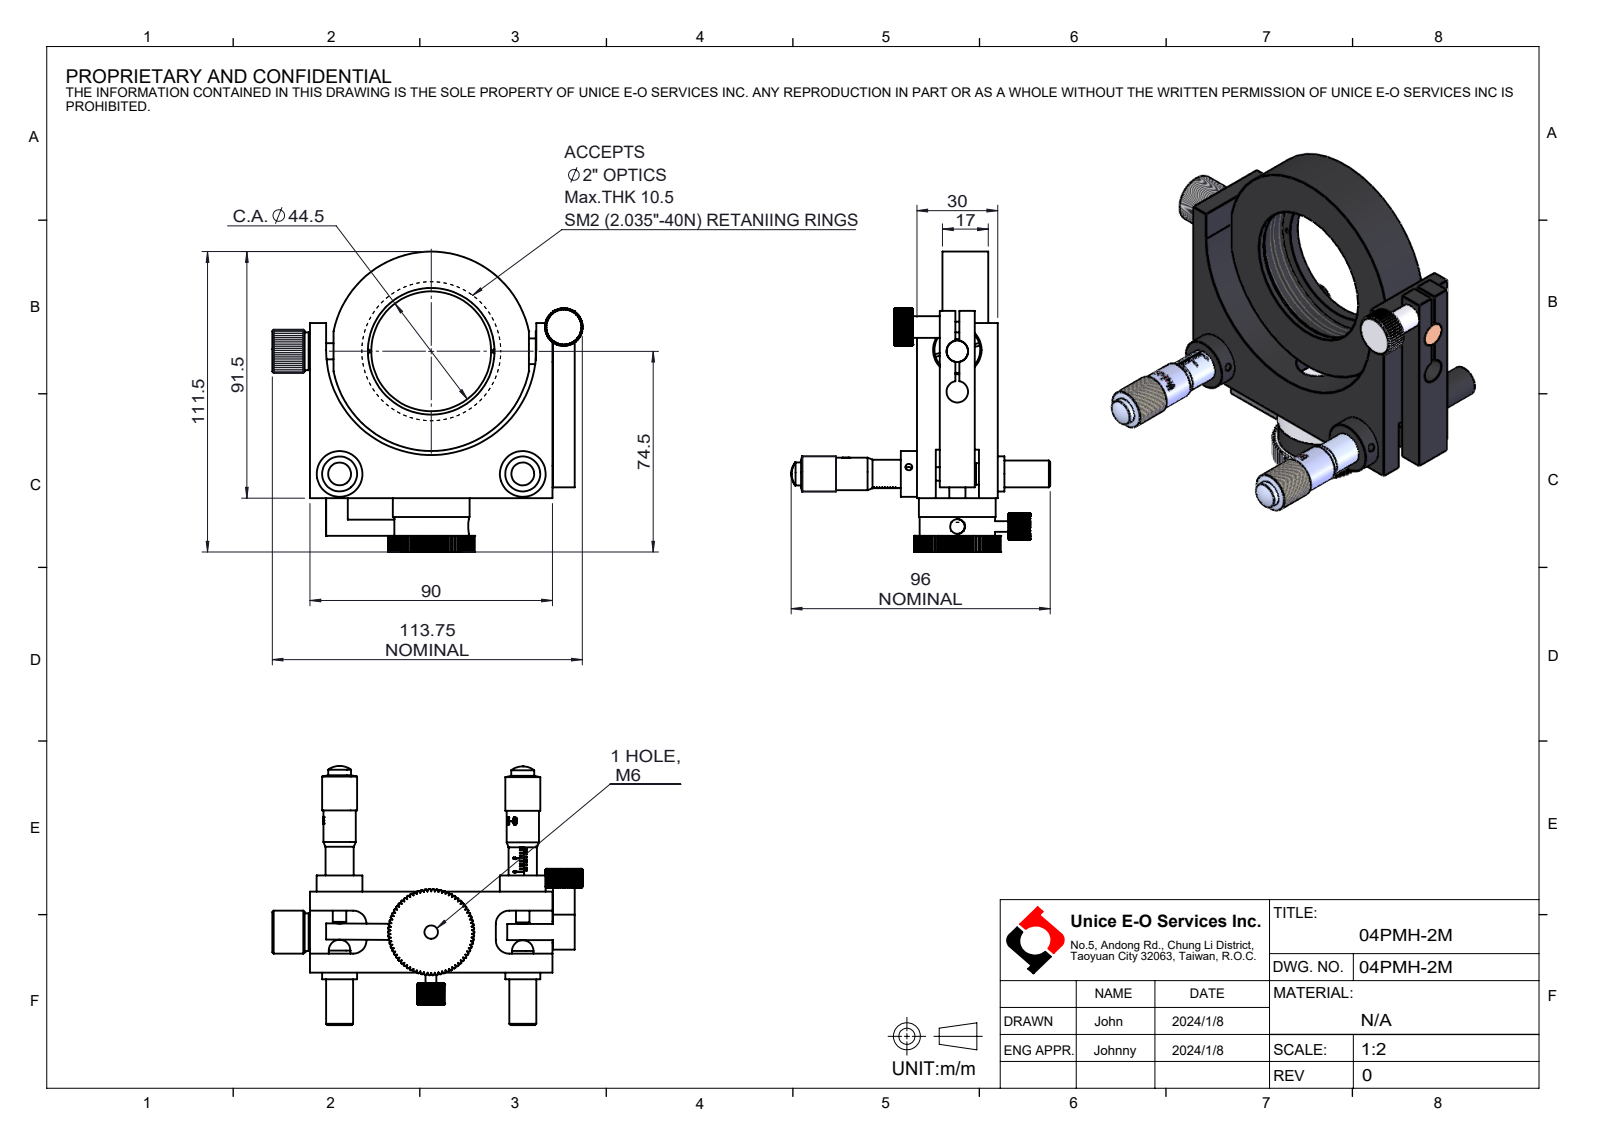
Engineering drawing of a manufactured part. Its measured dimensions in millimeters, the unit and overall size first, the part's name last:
Units: millimetres
Overall size (bounding box): 115.25 × 111.5 × 96.33
Round holes (diameter × count): ⌀2.5 ×4, ⌀5 ×4, ⌀3.4 ×3, ⌀8 ×3, ⌀1.5 ×2, ⌀3.3 ×2, ⌀6 ×2, ⌀6.3 ×2, ⌀8.5 ×2, ⌀9.5 ×2, ⌀10.6 ×2, ⌀12 ×2
Round bosses / shafts (diameter × count): ⌀14 ×4, ⌀17 ×3, ⌀13 ×2, ⌀12 ×2, ⌀10.5 ×2, ⌀10 ×2, ⌀9.9 ×2, ⌀9.2 ×2
Partial cylindrical surfaces — rounded edges, fillets, slot ends (radius × count): R5 ×5, R5.98 ×2, R7 ×1, R16 ×1, R39 ×1
Main face-to-face distances: 3.5, 9.5, 7, 6, 20.5, 17, 30, 26.5, 14, 8
Hole centre spacings: 0.5, 11, 23.5, 56.8, 22, 27.28, 46.68, 46.72
Volume: 147 407 mm³ · Surface area: 68 396 mm²
Bodies: 26 solids, 1785 faces (903 planar, 458 cylindrical, 424 other)
Part name (STEP PRODUCT): 04PMH-2M
STEP written by: SolidWorks 2024 (CONFIG_CONTROL_DESIGN)
